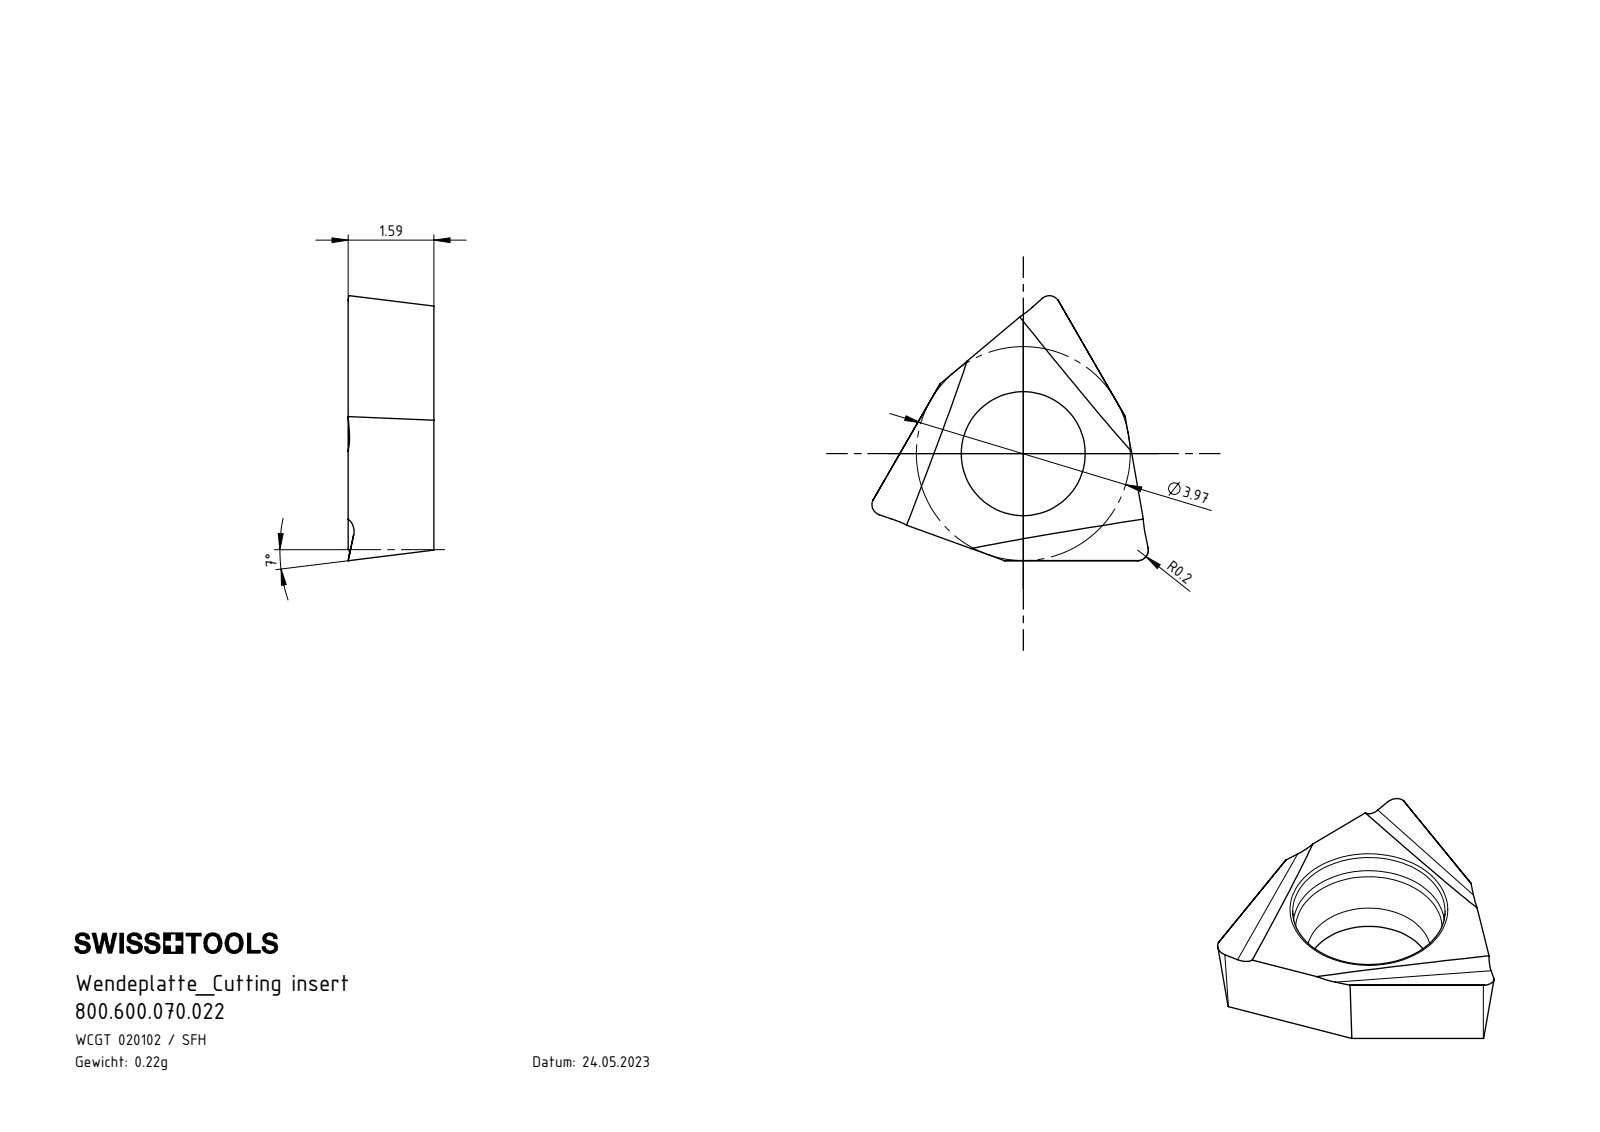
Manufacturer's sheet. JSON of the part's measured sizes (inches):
{"part_name": "WWA.U02.001.002", "step_written_by": "SolidWorks 2017 (AUTOMOTIVE_DESIGN)", "units": "inches", "bodies": {"solids": 1, "faces": 31, "planar": 14, "cylindrical": 5, "other": 12}, "overall_size": [0.202, 0.194, 0.063], "volume_in3": 0.001, "surface_area_in2": 0.087, "round_holes": [[0.091, 1]], "partial_cylinders_radius": [[0.012, 3]], "face_to_face_distances": [0.063]}
